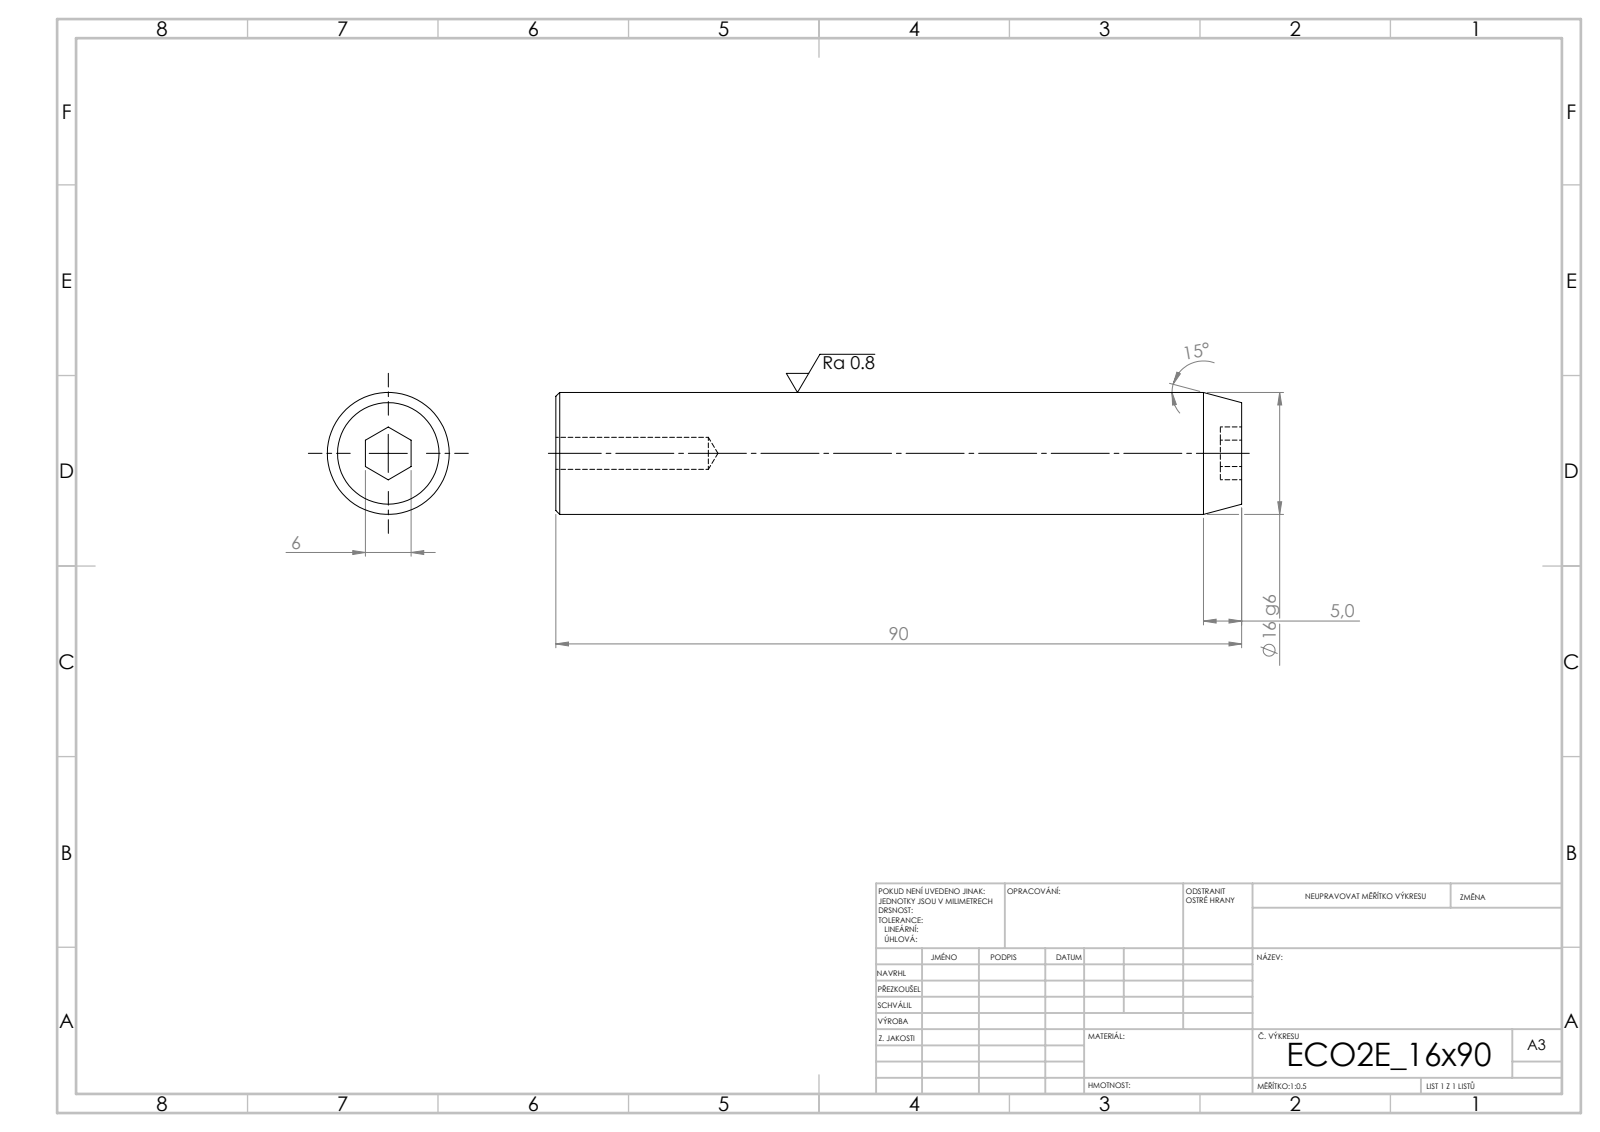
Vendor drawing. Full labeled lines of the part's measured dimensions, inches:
STEP written by: SolidWorks 2019 (CONFIG_CONTROL_DESIGN)
Units: inches
Bodies: 1 solid, 19 faces (9 planar, 4 cylindrical, 6 other)
Overall size (bounding box): 3.543 × 0.63 × 0.63
Volume: 1.072 in³ · Surface area: 8 in²
Round holes (diameter × count): ⌀0.165 ×1
Round bosses / shafts (diameter × count): ⌀0.63 ×1
Main face-to-face distances: 3.543, 0.11, 3.433, 0.236
